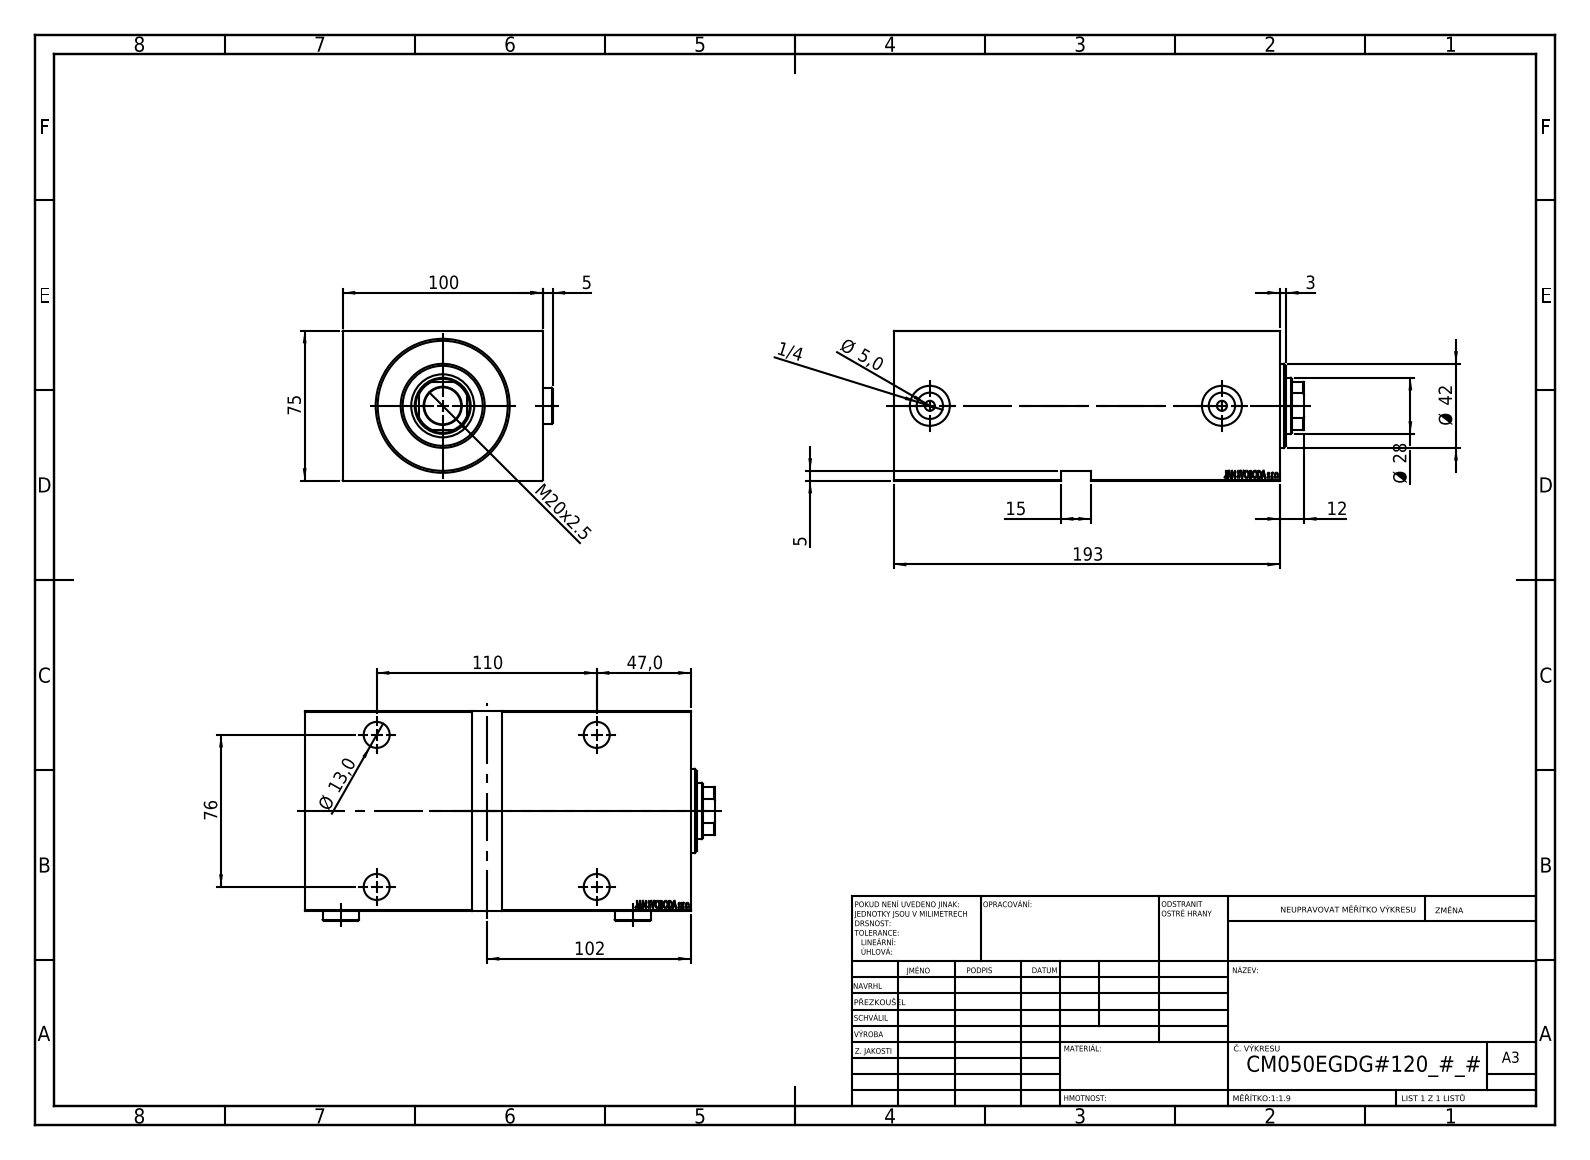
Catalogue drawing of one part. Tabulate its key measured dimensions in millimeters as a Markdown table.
| quantity | value |
| --- | --- |
| part name | V450CM_E_VCP; Zatka_OIL_PORT; V450CM_VC_B; V450CM_E_Body |
| STEP written by | SolidWorks 2019 (CONFIG_CONTROL_DESIGN) |
| units | millimeters |
| bodies | 5 solids, 912 faces (446 planar, 68 cylindrical, 398 other) |
| overall size | 205 × 104.9 × 75 |
| volume | 1 229 000 mm³ |
| surface area | 164 660 mm² |
| round holes (diameter × count) | 13 × 4, 19 × 4, 5 × 2, 13.16 × 2, 20 × 2, 18.5 × 1, 28 × 1, 31.5 × 1, 50 × 1, 65 × 1 |
| round bosses / shafts (diameter × count) | 18 × 2, 52 × 1, 42 × 1 |
| partial cylindrical surfaces (radius × count) | 13.5 × 1 |
| main face-to-face distances | 75, 100, 193, 5, 14, 179, 188, 174, 176.4, 162.4 |
| hole center spacings | 76, 110, 133.7, 146 |
